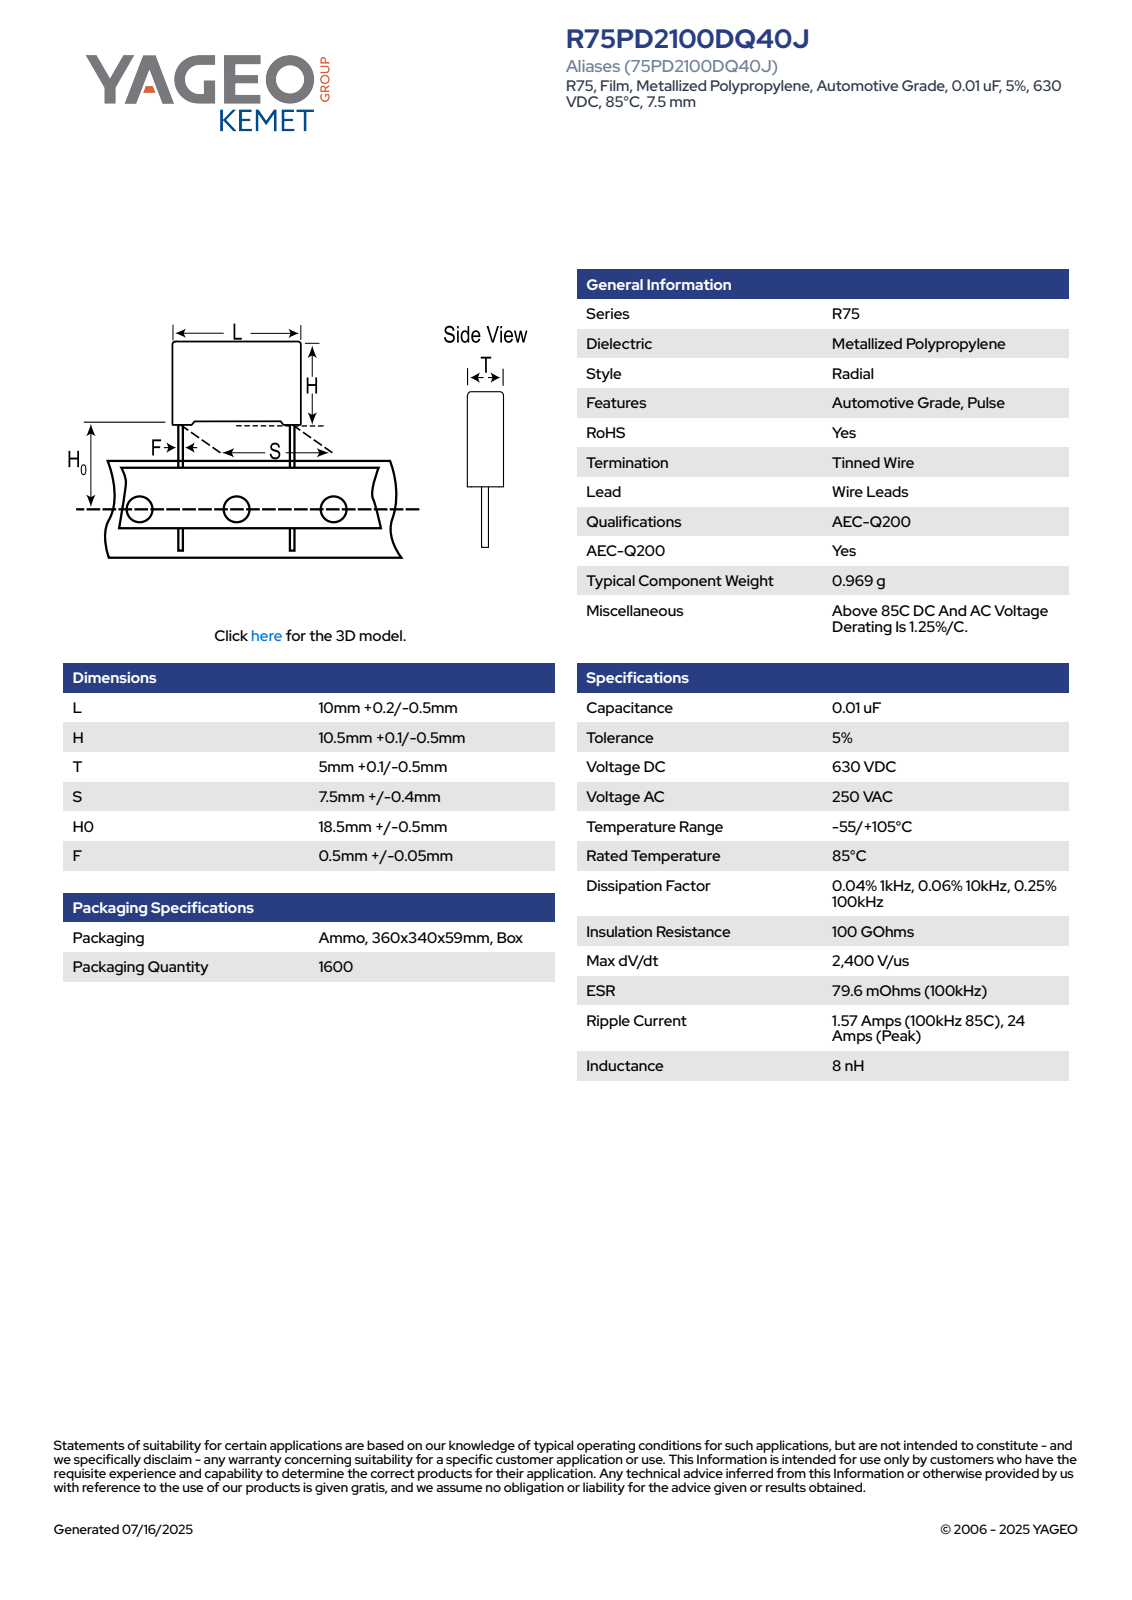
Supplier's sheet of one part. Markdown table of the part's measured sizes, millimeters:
| quantity | value |
| --- | --- |
| part name | CFR_RB2_10X10.5X5_L10.2H10.6T5.1S7.5H019F0.55 |
| STEP written by | SolidWorks 2020 (AUTOMOTIVE_DESIGN) |
| units | millimeters |
| bodies | 4 solids, 85 faces (77 planar, 8 cylindrical, 0 other) |
| overall size | 29.6 × 10.2 × 5.11 |
| volume | 527 mm³ |
| surface area | 513 mm² |
| round bosses / shafts (diameter × count) | 0.55 × 2 |
| partial cylindrical surfaces (radius × count) | 0.5 × 4 |
| main face-to-face distances | 5.1, 10.2, 9.85, 0.34, 4.76, 0.75, 10.6, 9.86, 4.42, 9.52 |
